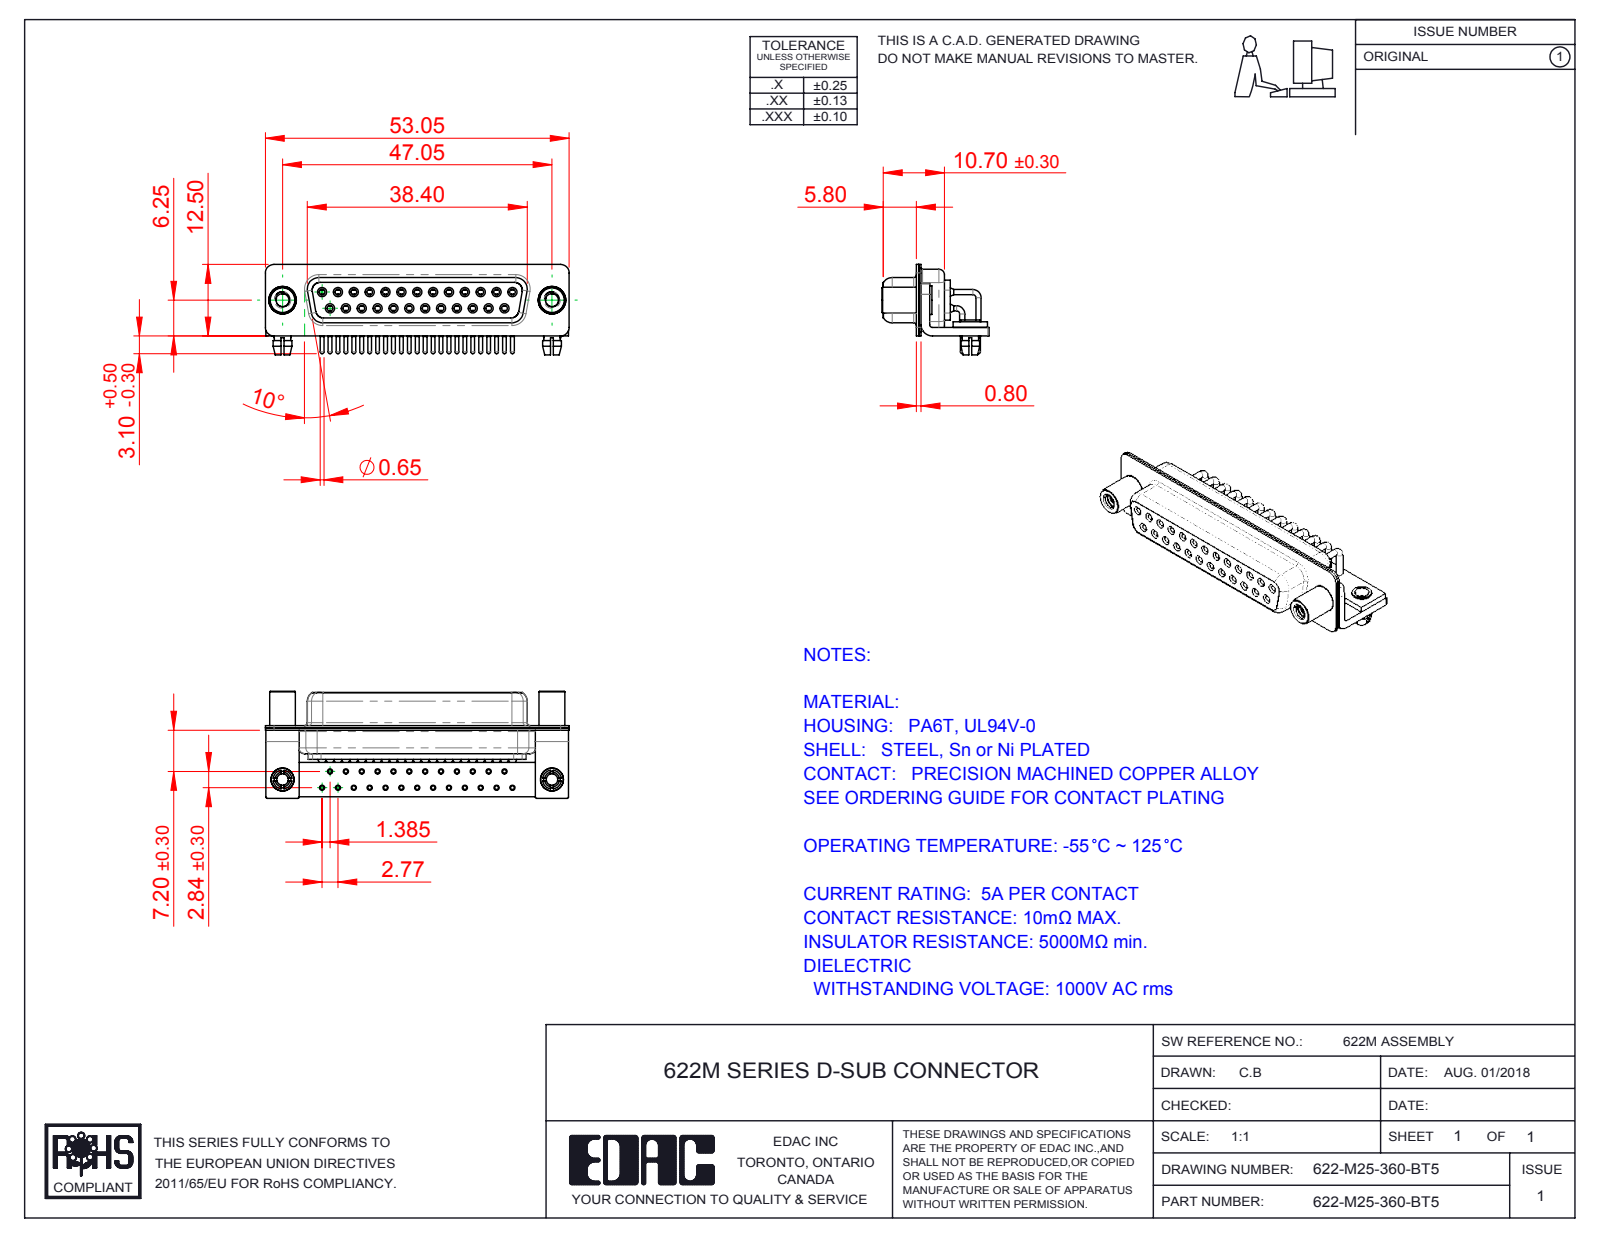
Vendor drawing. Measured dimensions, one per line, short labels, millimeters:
name: 622M Contact Row 1; 622M Shell Rear_25 Contacts; 622M Shell Front_25 Contacts; 622M Housing_25 Contacts (+6 more)
written by: SolidWorks 2016 (CONFIG_CONTROL_DESIGN)
unit: mm
bodies: 35 solids, 1846 faces (518 planar, 858 cylindrical, 470 other)
size: 53.05 × 18.7 × 15.8
volume: 4 535 mm³; area: 11 363 mm²
holes: 27× ⌀2, 25× ⌀0.9, 25× ⌀1, 25× ⌀1.1, 25× ⌀1.7, 25× ⌀1.8, 2× ⌀2.26, 2× ⌀2.5, 2× ⌀3.2, 2× ⌀4, 2× ⌀4.8
bosses: 27× ⌀0.9, 25× ⌀1.6, 25× ⌀1.5, 25× ⌀0.65, 2× ⌀5, 2× ⌀4.9, 2× ⌀4.5, 2× ⌀4
rounds: 16× R0.25, 16× R1.5, 13× R2, 8× R1.35, 8× R1.6, 5× R0.5, 4× R0.6, 4× R0.65
face distances: 0.4, 2.3, 1.9, 1.45, 8.95, 0.85, 0.8, 6.2, 9.35, 1
hole spacings: 3.16, 2.77, 5.54, 8.31, 11.08, 13.85, 16.62, 5.04
